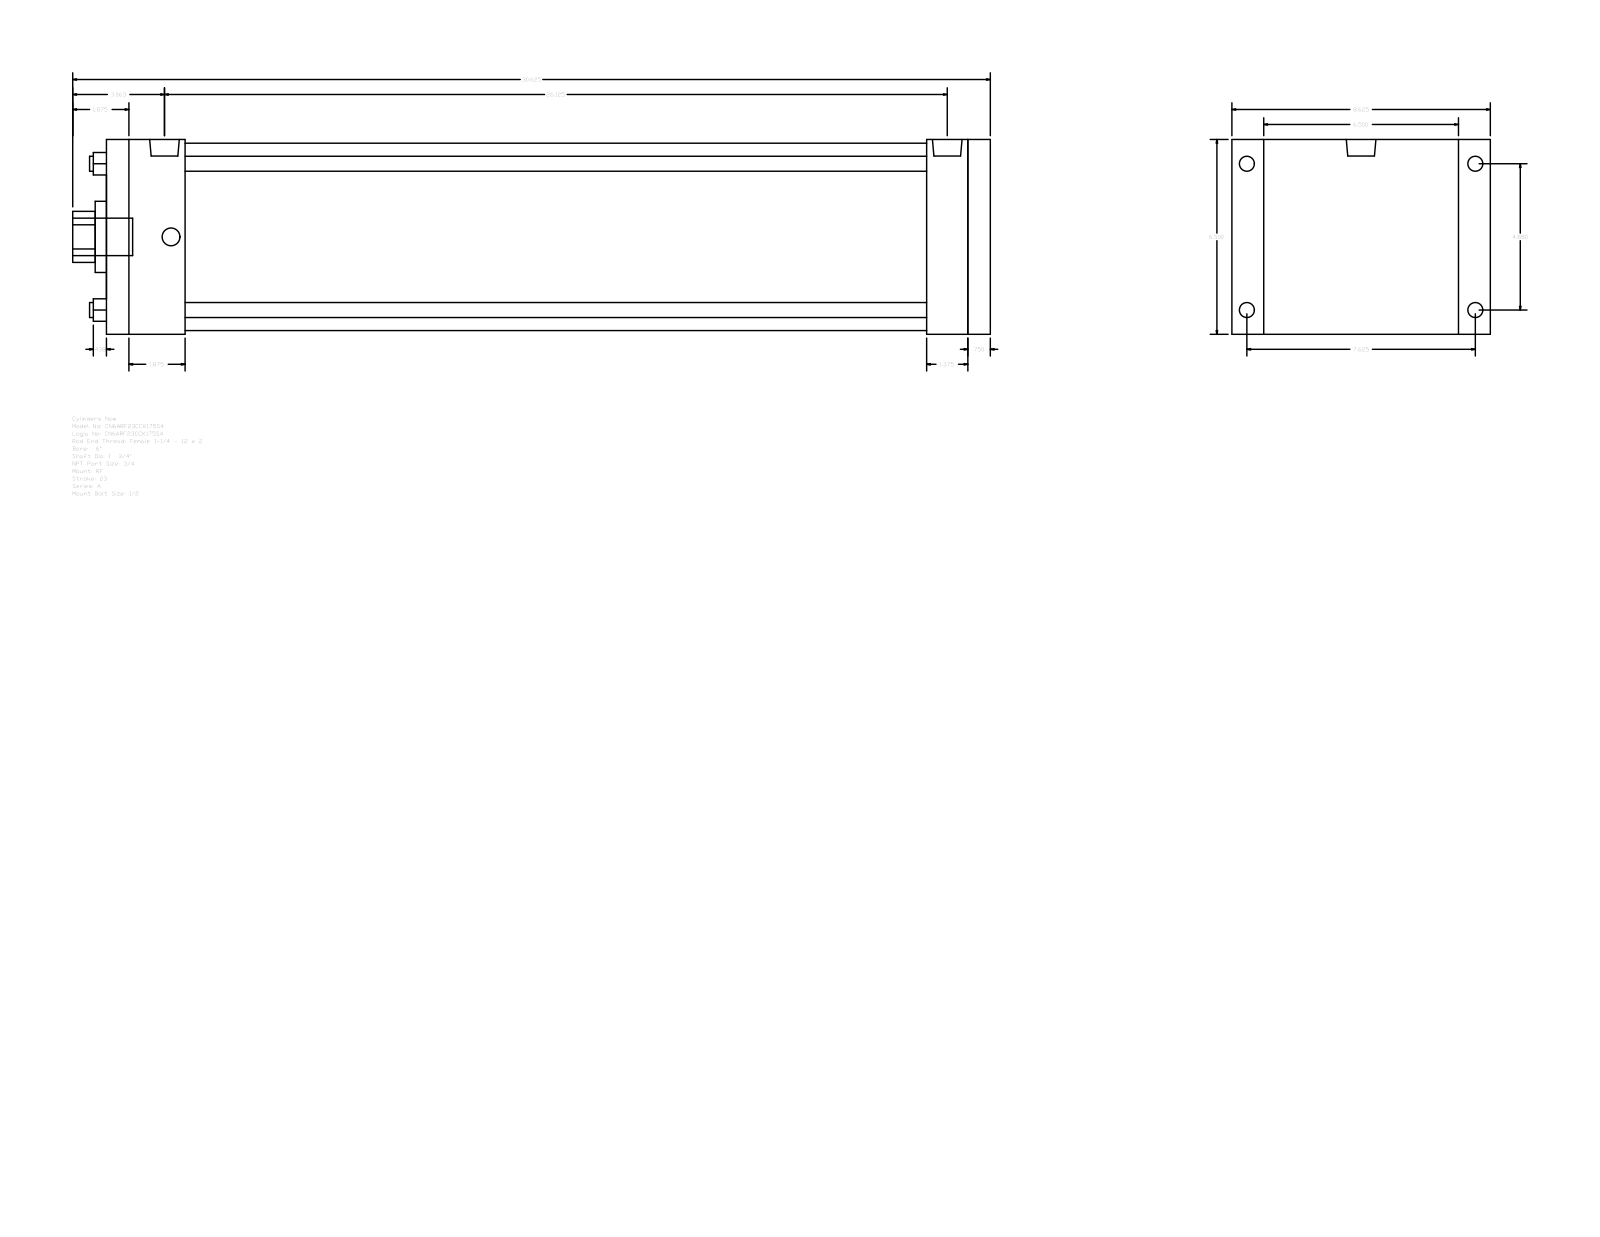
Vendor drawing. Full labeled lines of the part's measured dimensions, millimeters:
Part name (STEP PRODUCT): A_RF__0600_1.75
STEP written by: GSSL Pune (CONFIG_CONTROL_DESIGN)
Units: millimetres
Bodies: 0 solids, 92 faces (64 planar, 28 cylindrical, 0 other)
Overall size (bounding box): 777.88 × 219.07 × 165.1
Round holes (diameter × count): ⌀12.7 ×4, ⌀44.45 ×1, ⌀60.33 ×1, ⌀158.75 ×1
Round bosses / shafts (diameter × count): ⌀15.08 ×4, ⌀12.7 ×4, ⌀25.12 ×2, ⌀31.75 ×1
Partial cylindrical surfaces — rounded edges, fillets, slot ends (radius × count): R21.63 ×1
Main face-to-face distances: 165.1, 749.31, 19.05, 730.26, 66.68, 663.58, 682.63, 695.33, 628.65, 34.93
Hole centre spacings: 87.65, 123.96, 175.31
